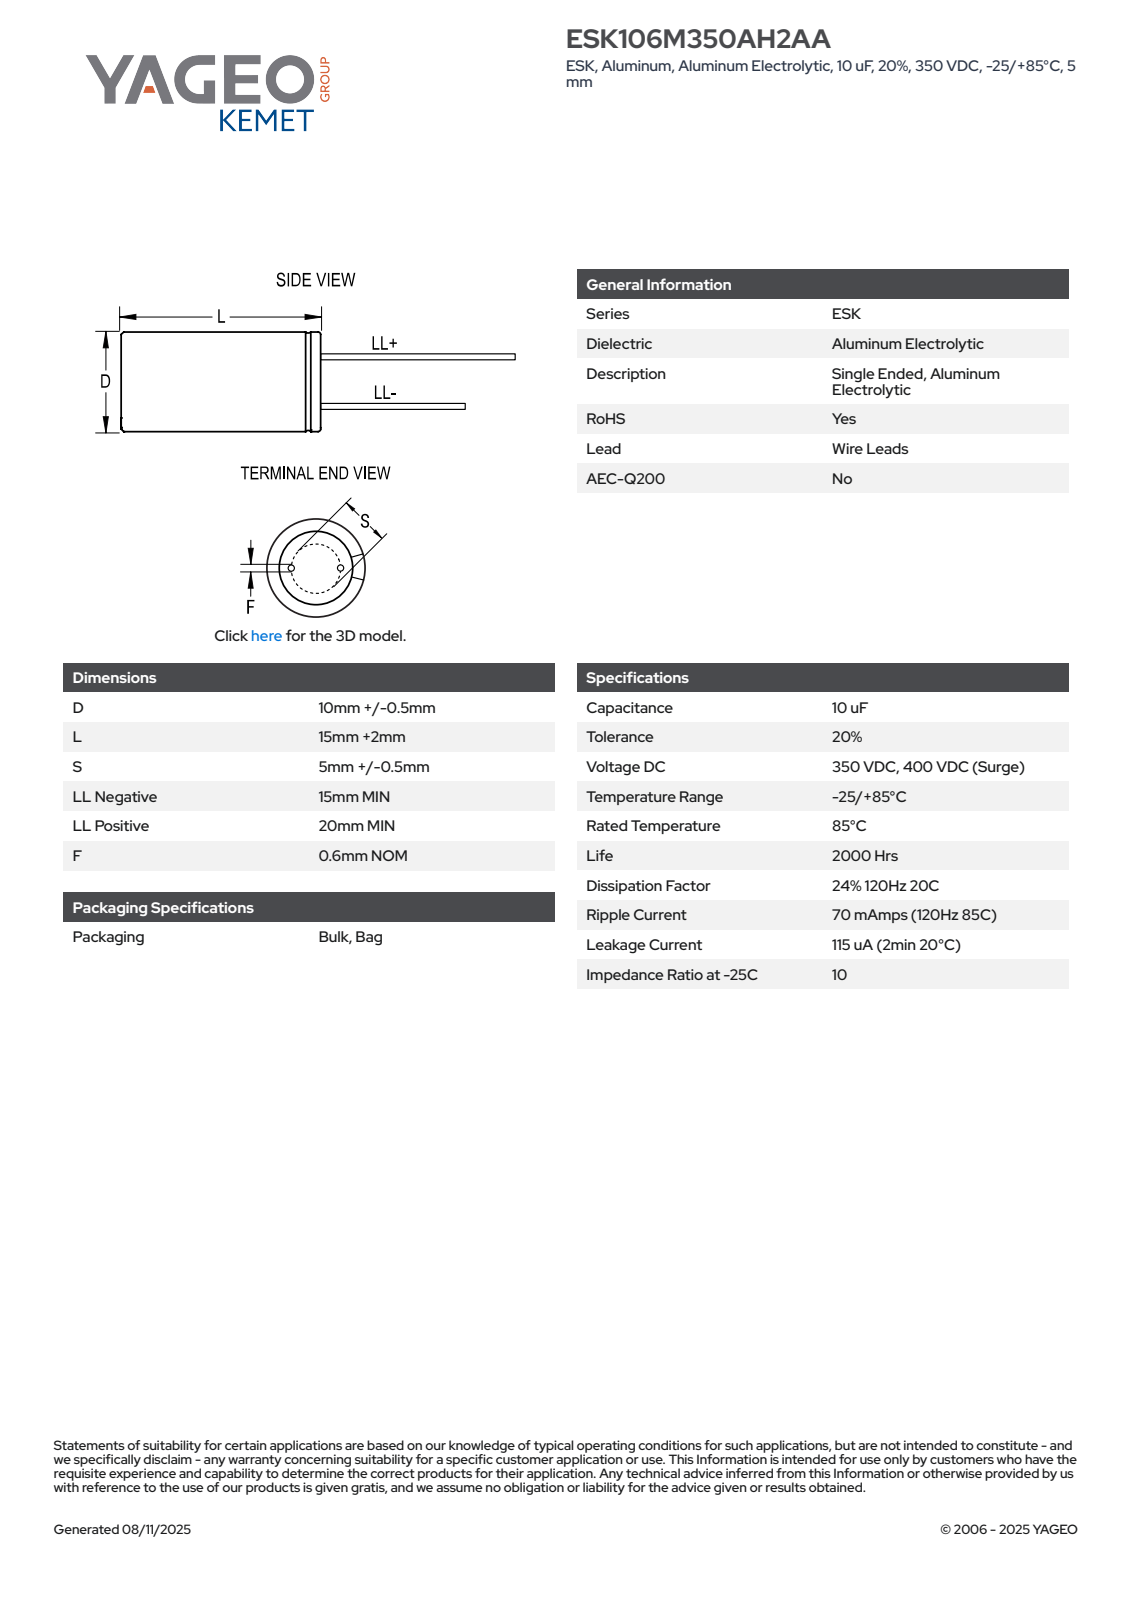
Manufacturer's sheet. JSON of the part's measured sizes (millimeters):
{"part_name": "CAR_KLP_10X15_D10.5L17S5F0.6", "step_written_by": "SolidWorks 2014 (AUTOMOTIVE_DESIGN)", "units": "millimeters", "bodies": {"solids": 4, "faces": 75, "planar": 61, "cylindrical": 8, "other": 6}, "overall_size": [37.01, 10.5, 10.5], "volume_mm3": 1470, "surface_area_mm2": 825, "round_bosses_or_shafts": [[0.6, 2], [10.5, 1]], "face_to_face_distances": [17, 17.01, 32.01, 37.01, 32, 37, 15, 20, 5, 1.41]}
